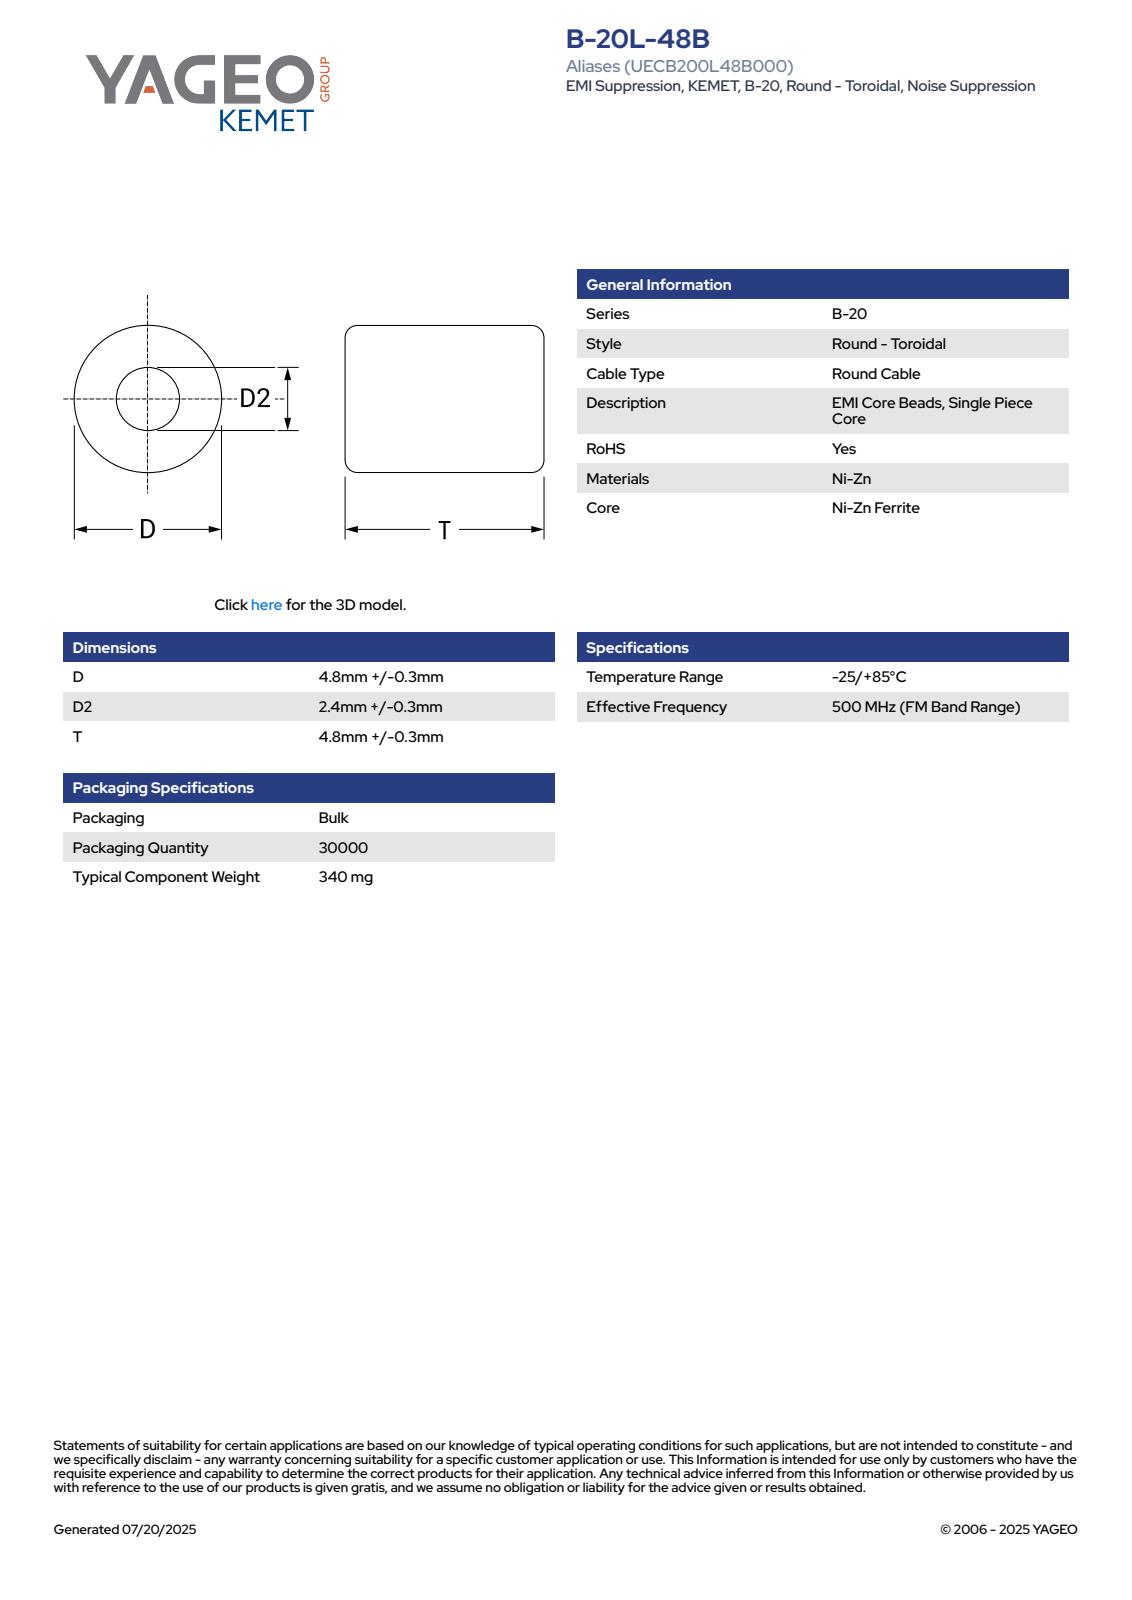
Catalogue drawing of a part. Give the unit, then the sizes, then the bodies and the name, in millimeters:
Units: millimetres
Overall size (bounding box): 5.11 × 5.1 × 5.1
Round holes (diameter × count): ⌀2.4 ×1
Round bosses / shafts (diameter × count): ⌀5.1 ×1
Partial cylindrical surfaces — rounded edges, fillets, slot ends (radius × count): R2.56 ×1
Main face-to-face distances: 5.1, 2.36, 2.74, 0.38, 2.43, 2.67, 0.31, 2.6, 2.5, 2.53
Volume: 81 mm³ · Surface area: 150 mm²
Bodies: 1 solid, 66 faces (25 planar, 7 cylindrical, 34 other)
Part name (STEP PRODUCT): EC_KBCH_D5.1D22.4T5.1
STEP written by: SolidWorks 2021 (AUTOMOTIVE_DESIGN)
